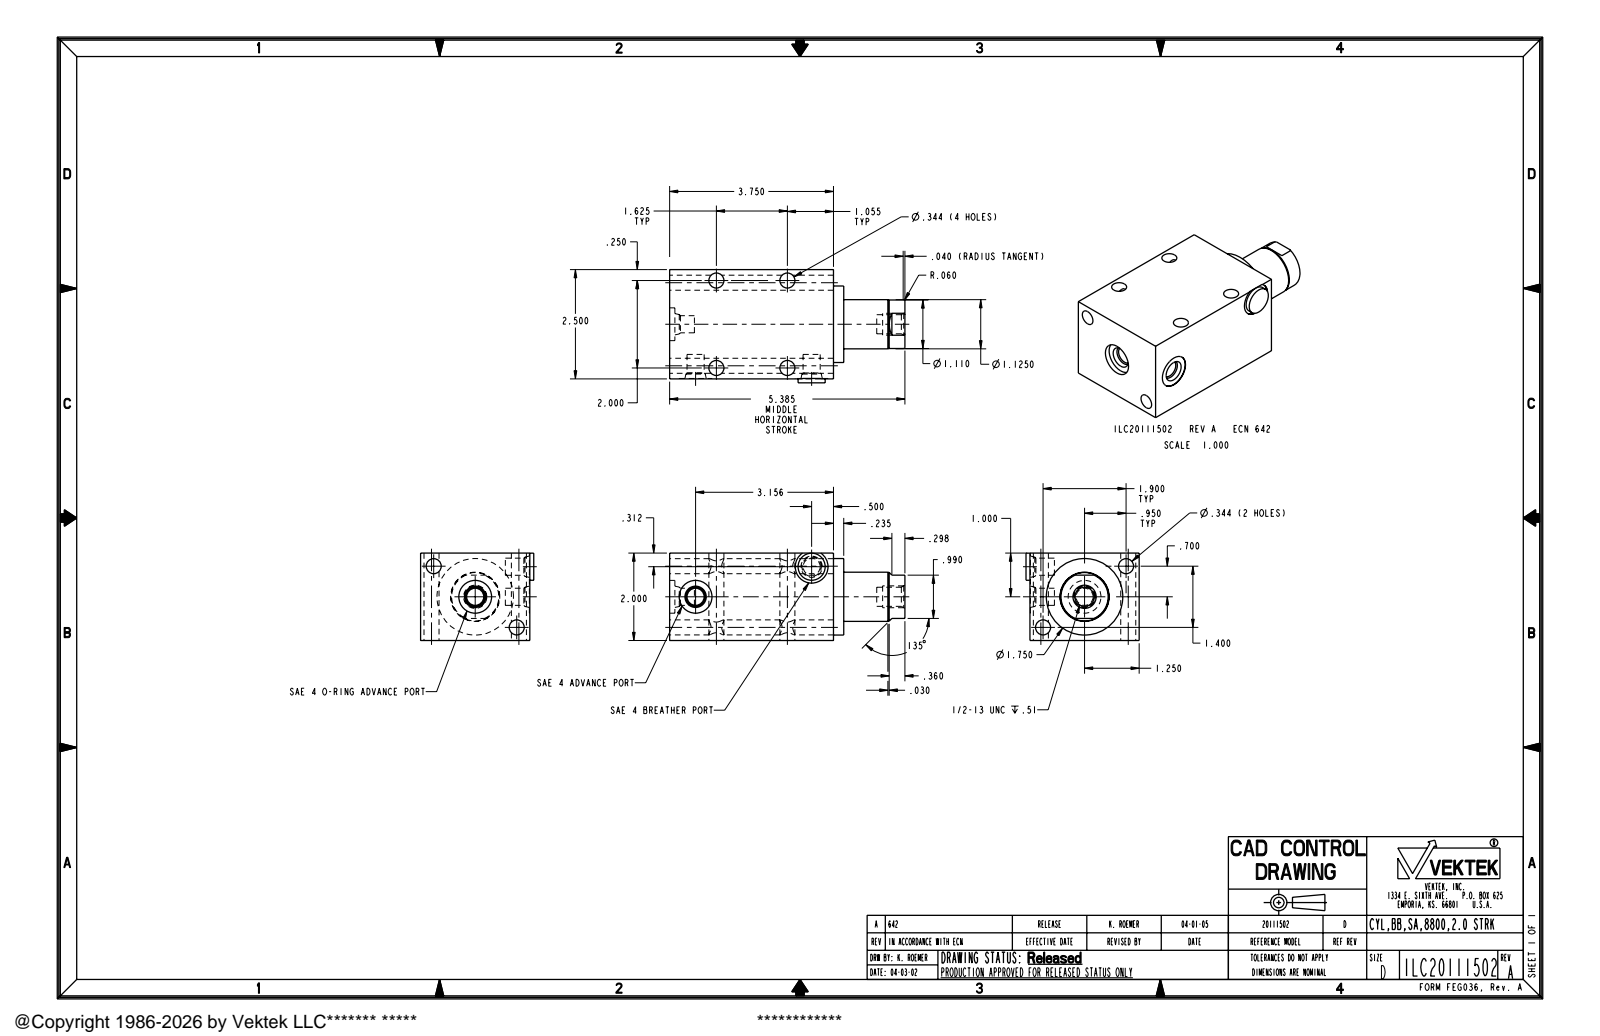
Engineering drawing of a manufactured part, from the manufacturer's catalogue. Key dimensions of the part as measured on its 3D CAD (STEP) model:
Part name (STEP PRODUCT): ILC20111502
STEP written by: PRO/ENGINEER BY PARAMETRIC TECHNOLOGY CORPORATION, 2004290 (AUTOMOTIVE_DESIGN_CC2)
Units: inches
Bodies: 1 solid, 83 faces (22 planar, 43 cylindrical, 18 other)
Overall size (bounding box): 5.385 × 2.59 × 2
Volume: 19.01 in³ · Surface area: 68.08 in²
Round holes (diameter × count): ⌀0.344 ×6, ⌀0.392 ×3, ⌀0.75 ×3, ⌀0.437 ×1
Round bosses / shafts (diameter × count): ⌀1.75 ×1, ⌀1.125 ×1, ⌀1.11 ×1, ⌀0.62 ×1, ⌀0.5 ×1
Main face-to-face distances: 2, 2.5, 3.75, 0.235, 3.985, 1.4, 1.635, 5.385, 2.49, 0.09
Hole centre spacings: 1.18, 1.625, 2, 2.577, 2.36, 2.744
